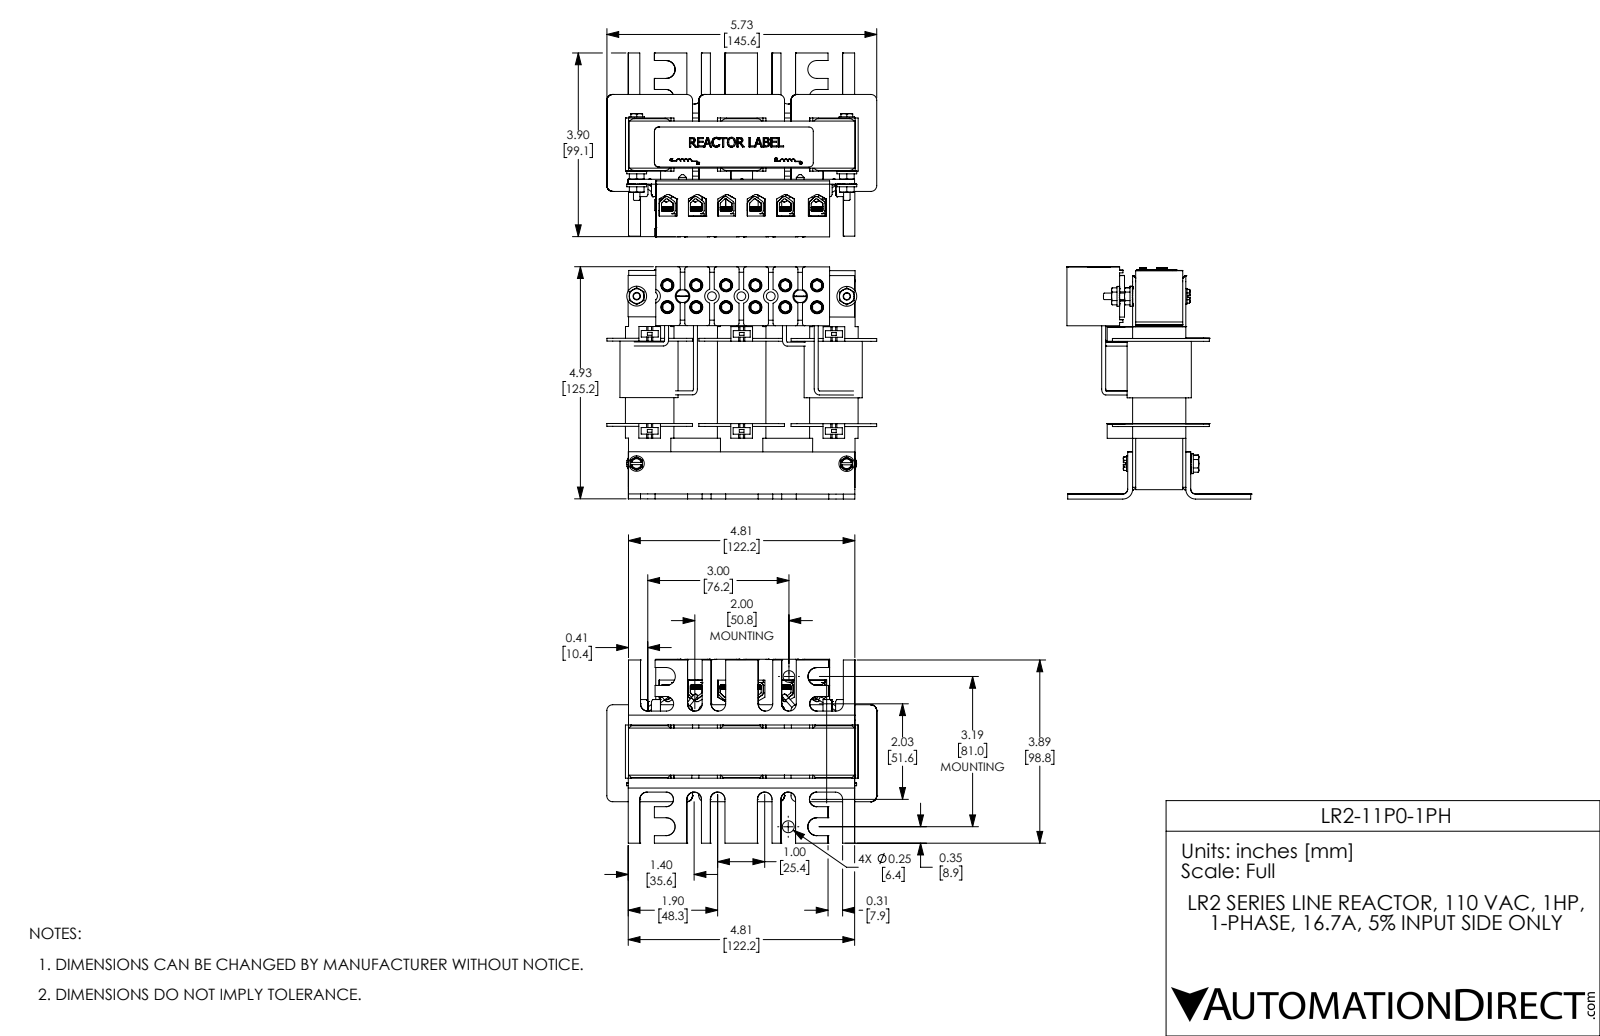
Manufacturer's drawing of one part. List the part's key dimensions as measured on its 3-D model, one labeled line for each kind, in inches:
Part name (STEP PRODUCT): LR-11P0-1PH LR-22P0-1PH LR-23P0-1PH CoordFix
STEP written by: SolidWorks 2017 (AUTOMOTIVE_DESIGN)
Units: inches
Bodies: 48 solids, 2839 faces (1572 planar, 902 cylindrical, 365 other)
Overall size (bounding box): 5.736 × 4.934 × 3.906
Volume: 28.06 in³ · Surface area: 369.8 in²
Round holes (diameter × count): ⌀0.276 ×16, ⌀0.14 ×6, ⌀0.177 ×6, ⌀0.186 ×5, ⌀0.31 ×5, ⌀0.097 ×4, ⌀0.138 ×4, ⌀0.16 ×4, ⌀0.164 ×2, ⌀0.19 ×2
Round bosses / shafts (diameter × count): ⌀0.26 ×12, ⌀0.25 ×12, ⌀0.204 ×12, ⌀0.085 ×5, ⌀0.422 ×4, ⌀0.328 ×4, ⌀0.318 ×4, ⌀0.085 ×3
Partial cylindrical surfaces — rounded edges, fillets, slot ends (radius × count): R0.029 ×24, R0.05 ×20, R0.125 ×20, R0.076 ×18, R0.155 ×17, R0.07 ×12, R0.075 ×12, R0.03 ×8
Main face-to-face distances: 0.065, 1.065, 1, 1.13, 0.06, 0.152, 0.105, 0.087, 1.81, 3.914
Hole centre spacings: 0.465, 0.378, 0.465, 0.635, 1.25, 1.328, 3.555, 3.84
